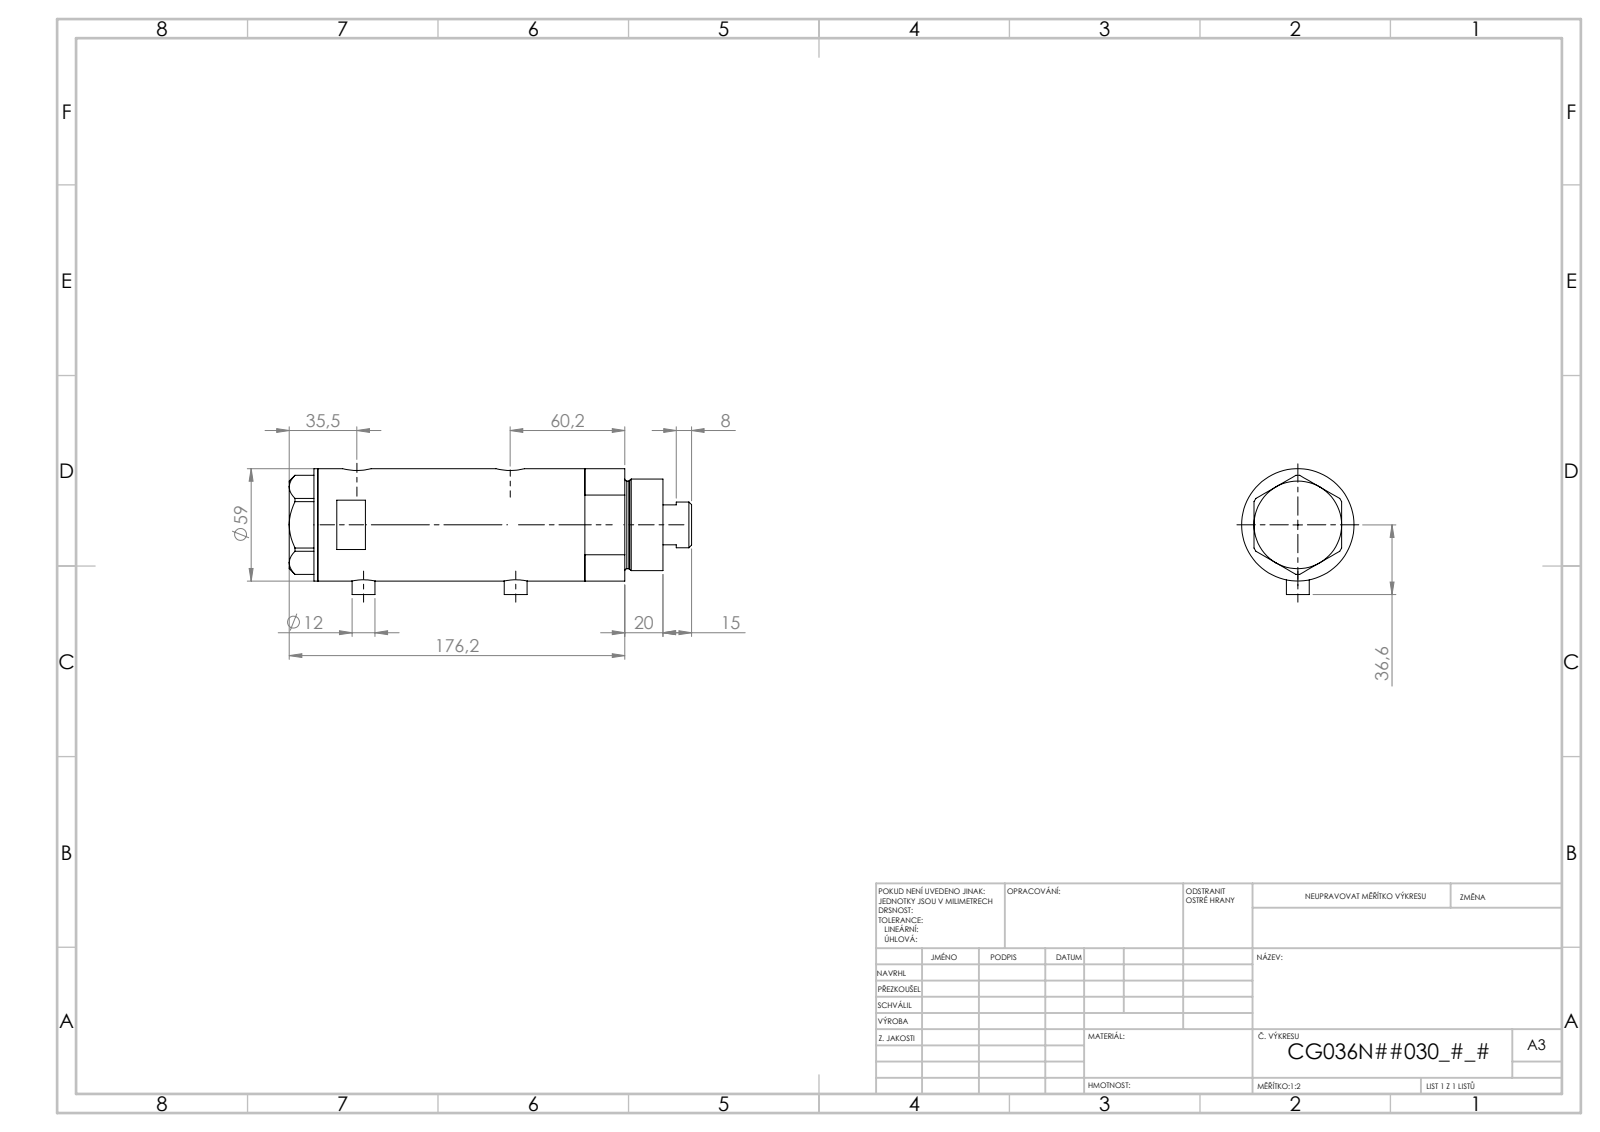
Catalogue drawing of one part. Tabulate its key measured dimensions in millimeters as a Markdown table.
| quantity | value |
| --- | --- |
| part name | V270CG_FRONT; V270CG_BACK; V270CG_VC; V270CG_MIDDLE |
| STEP written by | SolidWorks 2019 (CONFIG_CONTROL_DESIGN) |
| units | millimeters |
| bodies | 4 solids, 126 faces (53 planar, 53 cylindrical, 20 other) |
| overall size | 193.42 × 60.1 × 59 |
| volume | 437 351 mm³ |
| surface area | 93 203 mm² |
| round holes (diameter × count) | 5 × 2, 9.73 × 2, 12.5 × 2, 15 × 2, 8.5 × 1, 25 × 1, 26.5 × 1, 36 × 1, 40 × 1, 52 × 1 |
| round bosses / shafts (diameter × count) | 12 × 2, 59 × 1, 48 × 1, 46 × 1, 24 × 1 |
| main face-to-face distances | 87.34, 23.5, 63.84, 15, 38.5, 102.34, 178.42, 163.42, 139.92, 76.08 |
| hole center spacings | 2.9, 3.5, 62.15, 65.05, 65.65, 68.55, 2.89, 2.91 |
